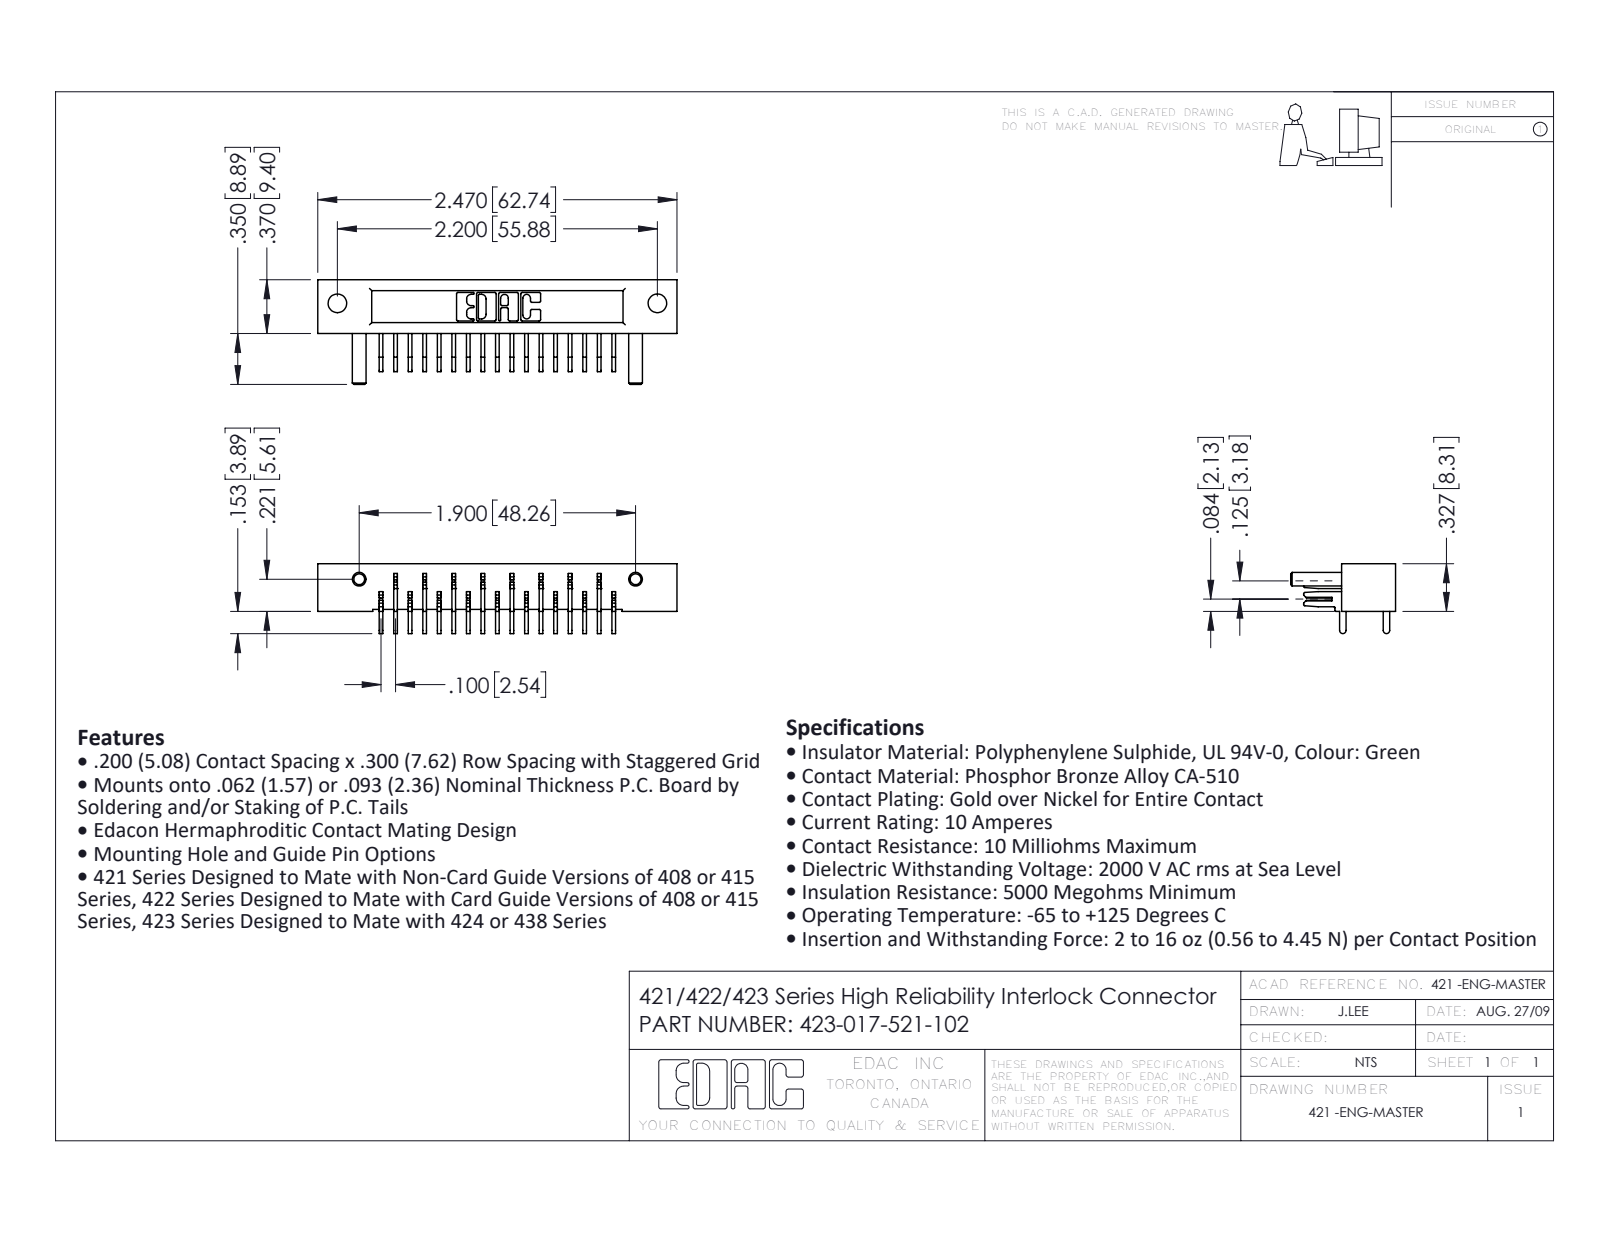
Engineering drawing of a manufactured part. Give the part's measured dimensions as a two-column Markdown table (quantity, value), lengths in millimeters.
| quantity | value |
| --- | --- |
| part name | 423 Part_17; 423-017-521-102; 421-290-002_121; 421-290-001_121 |
| STEP written by | SolidWorks 2016 (CONFIG_CONTROL_DESIGN) |
| units | millimeters |
| bodies | 18 solids, 643 faces (503 planar, 136 cylindrical, 4 other) |
| overall size | 62.7 × 18.3 × 12.2 |
| volume | 4 800 mm³ |
| surface area | 6 645 mm² |
| round holes (diameter × count) | 3.3 × 2 |
| round bosses / shafts (diameter × count) | 2.4 × 2 |
| partial cylindrical surfaces (radius × count) | 0.3 × 22, 0.2 × 6, 0.8 × 6, 0.2 × 4, 0.3 × 4, 0.4 × 4, 0.7 × 3, 0.6 × 2 |
| main face-to-face distances | 5.1, 10.2, 15.2, 0.6, 20.3, 5.7, 4.4, 25.4, 10.8, 9.5 |
| hole center spacings | 55.9 |
